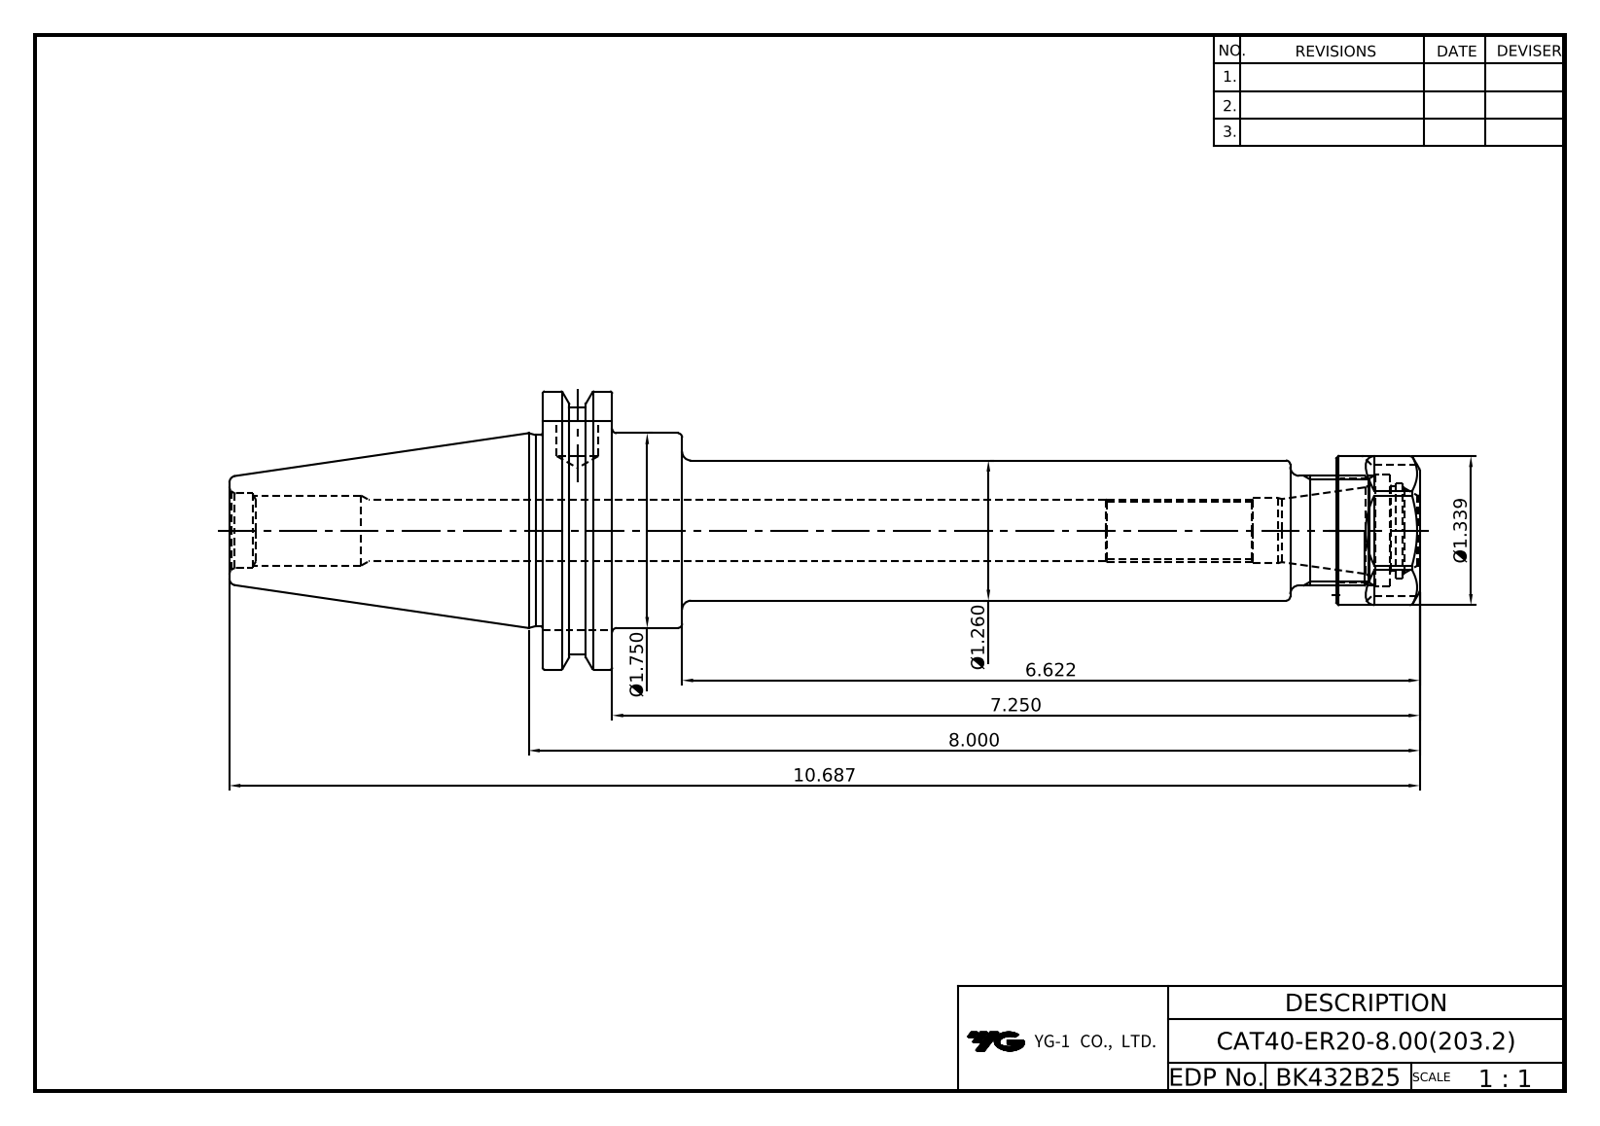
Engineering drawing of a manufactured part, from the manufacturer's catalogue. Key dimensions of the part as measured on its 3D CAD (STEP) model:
Part name (STEP PRODUCT): LO-CAT40-ER20-203.2; ER20NUT
STEP written by: Autodesk Inventor 2025 (AUTOMOTIVE_DESIGN)
Units: millimetres
Bodies: 2 solids, 92 faces (49 planar, 22 cylindrical, 21 other)
Overall size (bounding box): 271.45 × 63.5 × 61.09
Volume: 231 094 mm³ · Surface area: 50 084 mm²
Round holes (diameter × count): ⌀9.53 ×1, ⌀12.57 ×1, ⌀13.39 ×1, ⌀14.9 ×1, ⌀16 ×1, ⌀16.3 ×1, ⌀18.4 ×1, ⌀21.76 ×1, ⌀23.5 ×1, ⌀25.5 ×1
Round bosses / shafts (diameter × count): ⌀63.5 ×1, ⌀56.3 ×1, ⌀44.45 ×1, ⌀43.6 ×1, ⌀34 ×1, ⌀32 ×1, ⌀25 ×1
Main face-to-face distances: 15.88, 31.83, 15.95, 200.03, 184.15, 168.2, 19, 181.03, 165.15, 149.2
